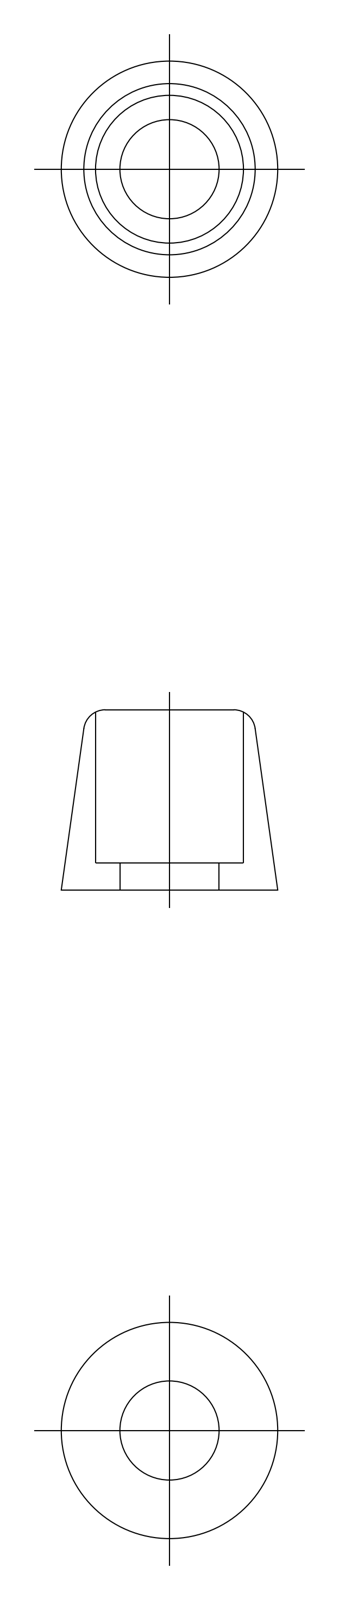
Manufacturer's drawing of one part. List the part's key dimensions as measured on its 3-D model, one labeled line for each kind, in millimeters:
Part name (STEP PRODUCT): facing ring
STEP written by: CADfix (AUTOMOTIVE_DESIGN)
Units: millimetres
Bodies: 1 solid, 10 faces (0 planar, 0 cylindrical, 10 other)
Overall size (bounding box): 12 × 12 × 10
Volume: 423 mm³ · Surface area: 712 mm²
